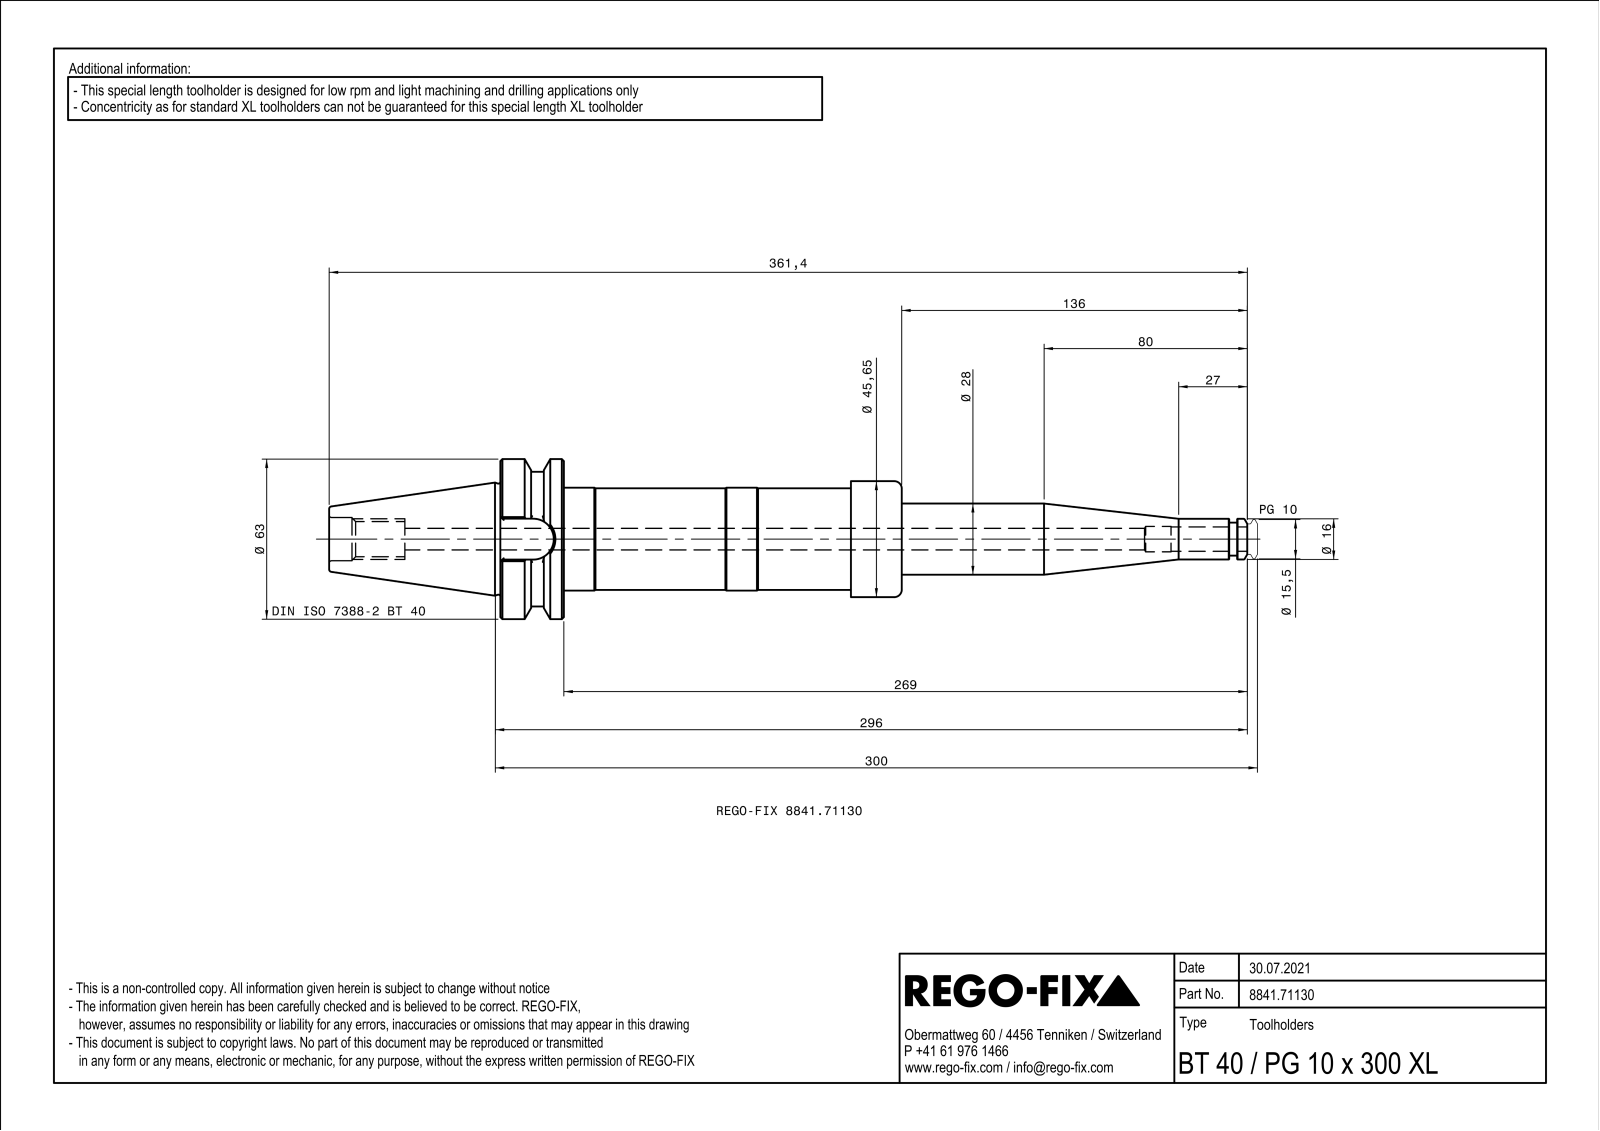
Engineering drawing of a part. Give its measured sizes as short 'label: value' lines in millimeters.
name: NOCUT
written by: SIEMENS PLM Software Solid Edge ST10 (AUTOMOTIVE_DESIGN)
unit: mm
bodies: 1 solid, 153 faces (52 planar, 36 cylindrical, 65 other)
size: 361.4 × 63 × 63
volume: 322 222 mm³; area: 66 414 mm²
holes: 1× ⌀9, 1× ⌀10, 1× ⌀13.84, 1× ⌀17, 1× ⌀25, 1× ⌀29, 1× ⌀38.38, 1× ⌀40.05, 1× ⌀43.3
bosses: 1× ⌀63, 1× ⌀53, 1× ⌀45.65, 1× ⌀40.5, 1× ⌀40, 1× ⌀34, 1× ⌀33, 1× ⌀28
rounds: 4× R0.5, 1× R8.05, 1× R22.77
face distances: 25, 133, 158, 6, 14, 138, 1.5, 131.5, 156.5, 20
